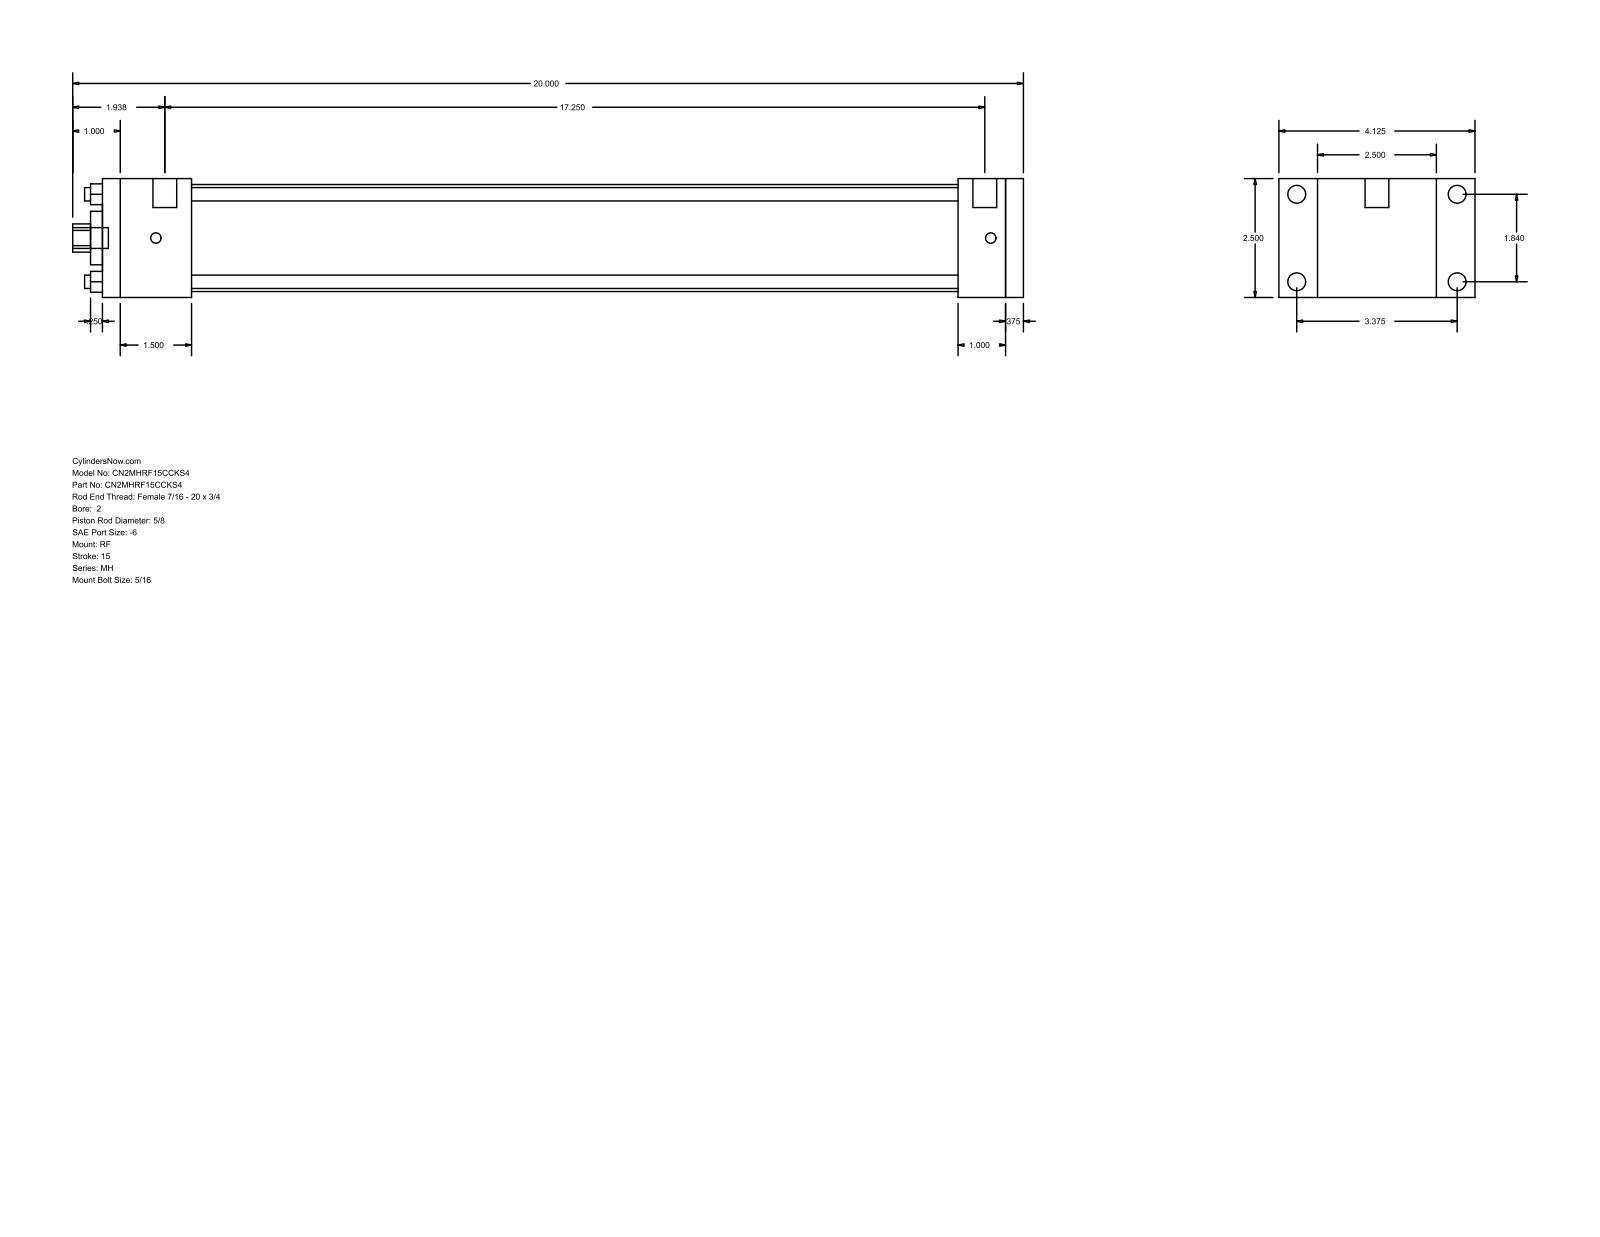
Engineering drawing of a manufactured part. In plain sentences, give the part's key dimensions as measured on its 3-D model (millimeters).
The part is named "MH_RF__0200_0.625". Its 3-D file was written by "GSSL Pune (CONFIG_CONTROL_DESIGN)". It is 0 solids with 92 faces: 64 planar, 28 cylindrical and 0 other. Overall it measures 508 by 104.78 by 63.5 millimeters. Round holes: 4 of diameter 7.14, 1 of diameter 15.88, 1 of diameter 28.57, 1 of diameter 57.15. Round bosses or shafts: 4 of diameter 9.53, 4 of diameter 5.56, 2 of diameter 12.7, 1 of diameter 11.11. Partial cylindrical surfaces (rounded edges, fillets, slot ends): 1 of radius 7.54. The main face-to-face distances are 63.5, 492.12, 9.52, 482.6, 47.62, 457.19, 409.57, 434.98, 444.5, 25.41. The hole center spacings are 33.05, 46.74, 66.1.
